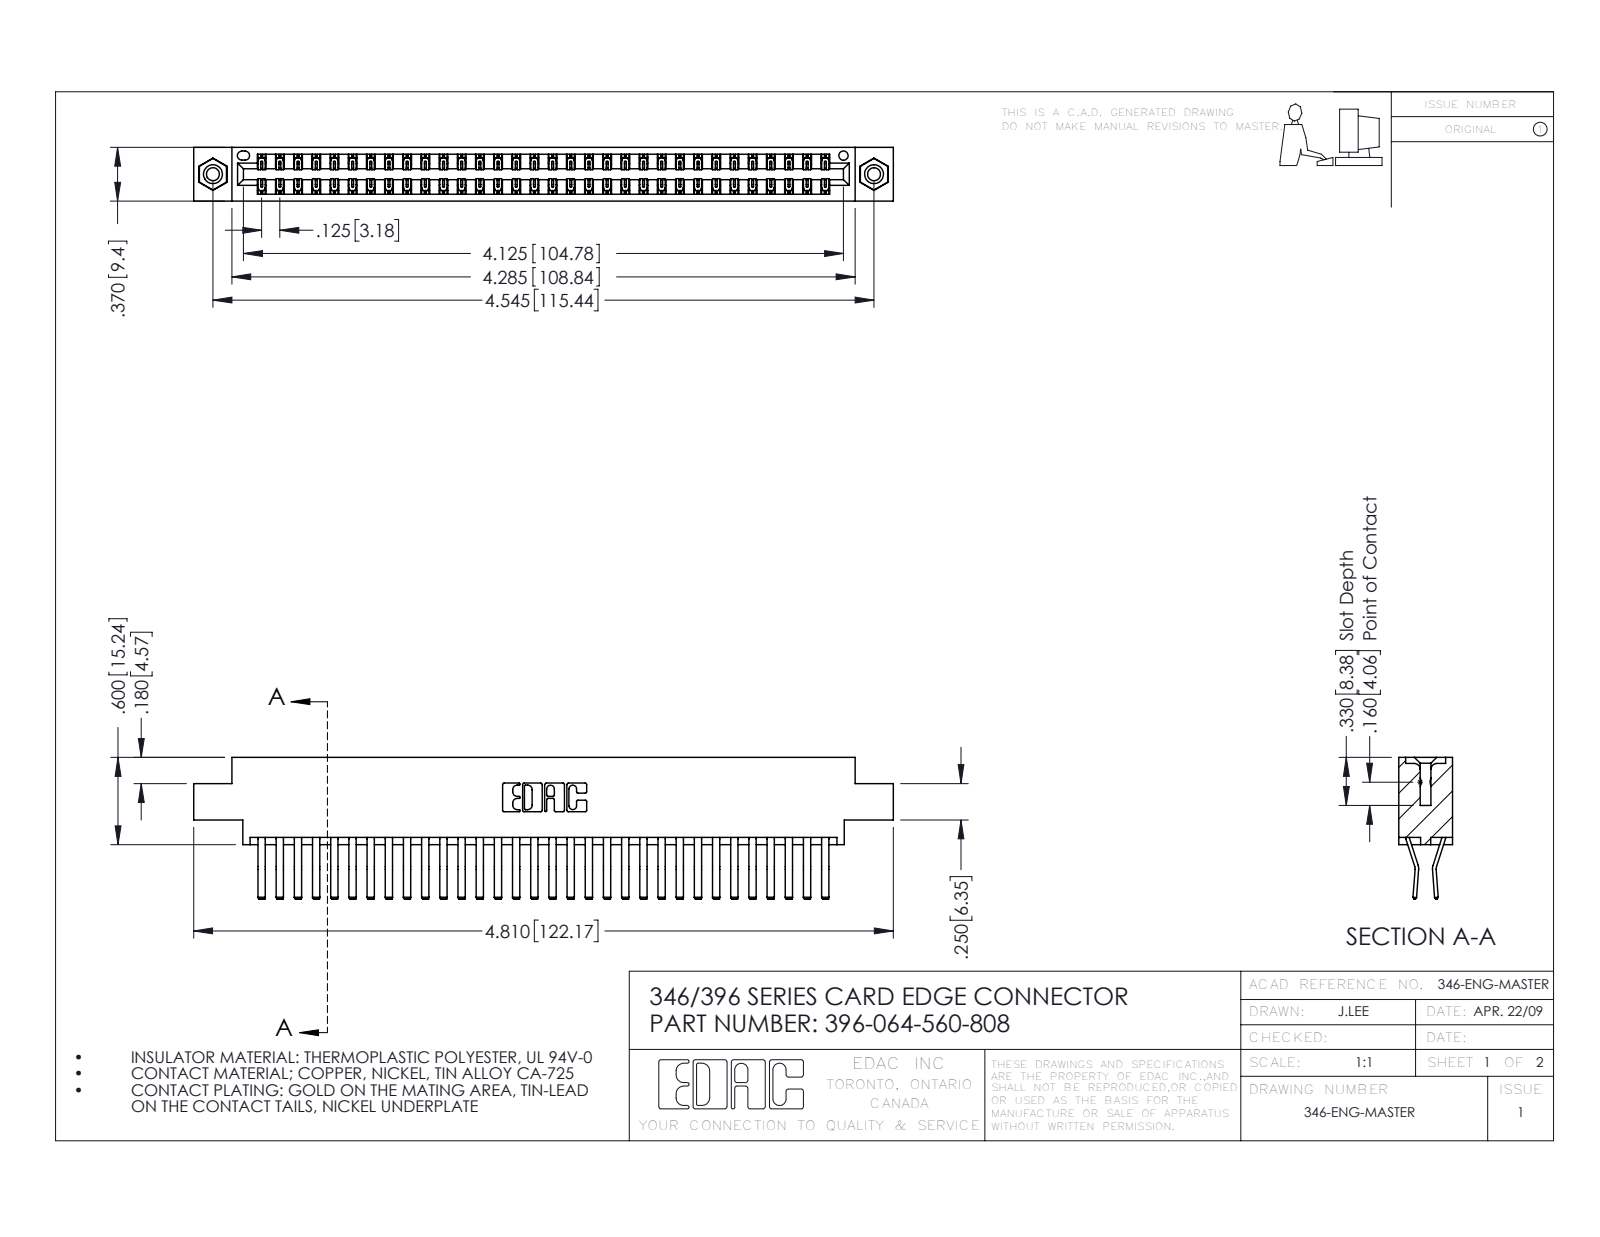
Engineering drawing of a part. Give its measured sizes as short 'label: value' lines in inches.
name: 396-064-560-808; 345-250-001_345-250-003-102; 346 Part_0.170 Offset - 0.156 Dia-TI; 345-292-001_560 Tail
written by: SolidWorks 2016 (CONFIG_CONTROL_DESIGN)
unit: in
bodies: 67 solids, 3642 faces (2352 planar, 1274 cylindrical, 16 other)
size: 4.81 × 0.975 × 0.37
volume: 0.738 in³; area: 27.57 in²
holes: 2× ⌀0.089, 2× ⌀0.125, 2× ⌀0.156, 1× ⌀0.064
bosses: 2× ⌀0.155
rounds: 96× R0.006, 22× R0.01, 6× R0.007, 6× R0.031, 3× R0.026, 2× R0.01, 2× R0.014, 2× R0.022
face distances: 0.048, 0.322, 0.37, 0.025, 0.25, 0.072, 0.298, 0.275, 0.222, 0.148
hole spacings: 0.246, 4.337, 4.545
